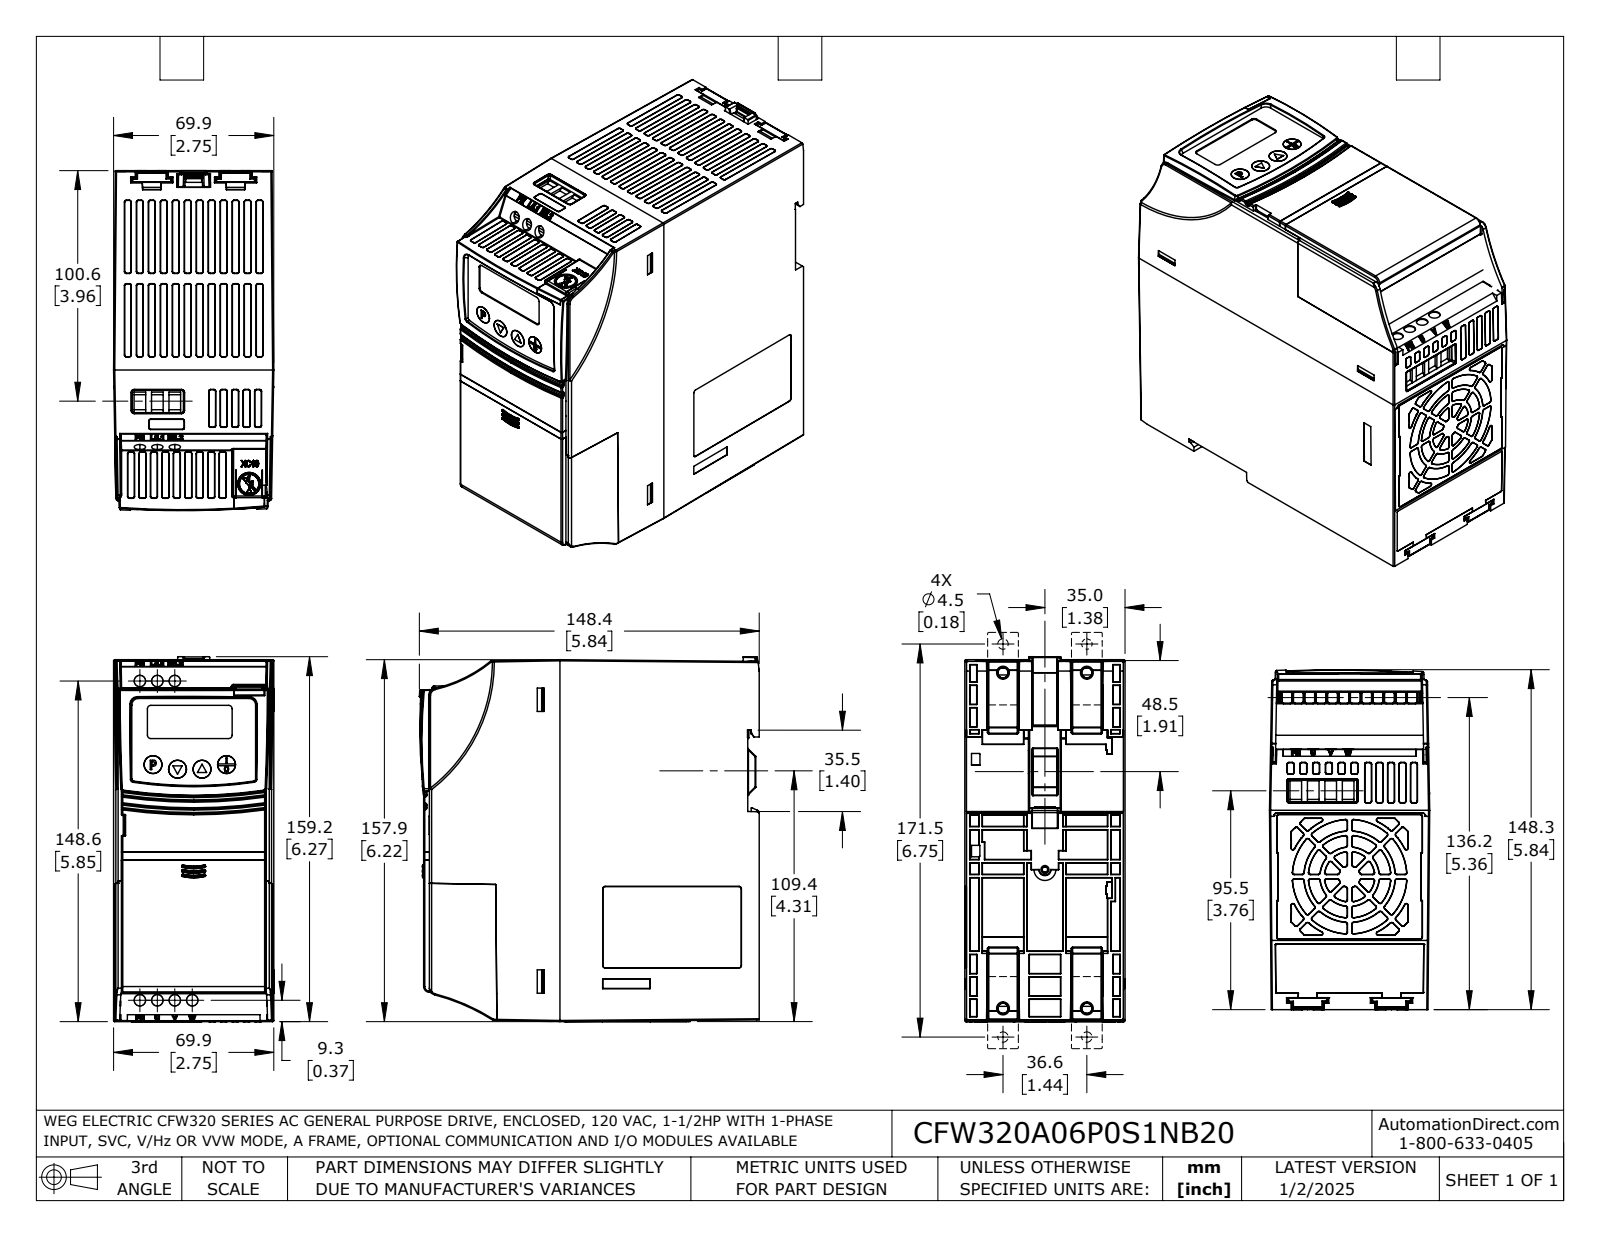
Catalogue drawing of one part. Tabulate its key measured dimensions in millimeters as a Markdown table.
| quantity | value |
| --- | --- |
| part name | CFW320A06P0S1NB20 |
| STEP written by | SolidWorks 2021 (AUTOMOTIVE_DESIGN) |
| units | millimeters |
| bodies | 6 solids, 3715 faces (1587 planar, 853 cylindrical, 1275 other) |
| overall size | 159.2 × 148.4 × 70 |
| volume | 249 700 mm³ |
| surface area | 199 400 mm² |
| round holes (diameter × count) | 5 × 3 |
| partial cylindrical surfaces (radius × count) | 0.3 × 327, 0.5 × 150, 1 × 13, 0.8 × 5, 3 × 3, 0.3 × 2, 2.5 × 1, 3.2 × 1 |
| main face-to-face distances | 1.8, 1.4, 0.5, 1.3, 152.4, 135.4, 134, 141.5, 140.1, 6.1 |
| hole center spacings | 7.6, 15.2 |
